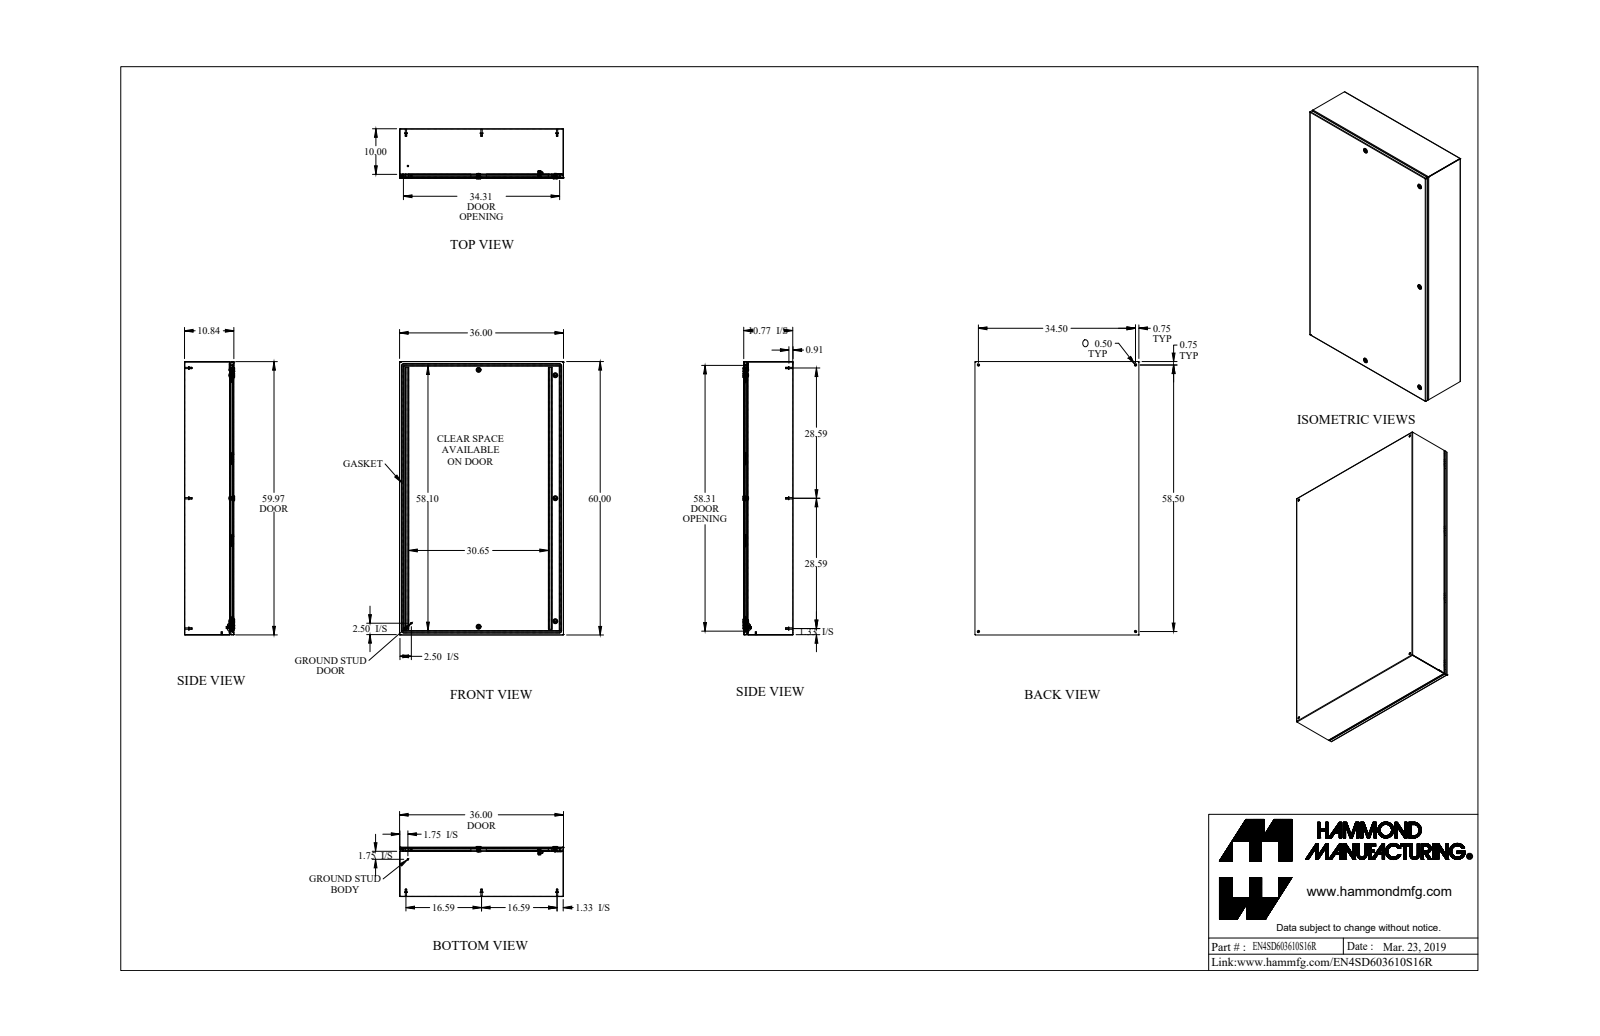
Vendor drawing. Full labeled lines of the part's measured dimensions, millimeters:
Part name (STEP PRODUCT): EN4SD603610S16R
STEP written by: SolidWorks 2018 (AUTOMOTIVE_DESIGN)
Units: millimetres
Bodies: 64 solids, 1721 faces (896 planar, 548 cylindrical, 277 other)
Overall size (bounding box): 1524 × 914.4 × 279.5
Volume: 8 484 000 mm³ · Surface area: 9 484 000 mm²
Round holes (diameter × count): ⌀12.7 ×9, ⌀5 ×5, ⌀9.8 ×5, ⌀16 ×5, ⌀19.5 ×5, ⌀4.4 ×1, ⌀5 ×1, ⌀6.1 ×1, ⌀6.1 ×1, ⌀7 ×1, ⌀9.5 ×1
Round bosses / shafts (diameter × count): ⌀8 ×10, ⌀15.9 ×9, ⌀7 ×8, ⌀27.9 ×5, ⌀15.9 ×5, ⌀6 ×5, ⌀19.9 ×3, ⌀13.3 ×3
Partial cylindrical surfaces — rounded edges, fillets, slot ends (radius × count): R1.1 ×24, R0.9 ×20, R2.7 ×20, R1.6 ×18, R2.4 ×10, R3.2 ×10, R0.4 ×9, R0.2 ×8
Main face-to-face distances: 1.8, 273.6, 271.7, 275.4, 912.6, 910.7, 914.4, 1.8, 1522.2, 1524
Hole centre spacings: 422.5, 428.8, 455.4, 743.4, 851.3, 876.3, 1128.4, 1465.2
